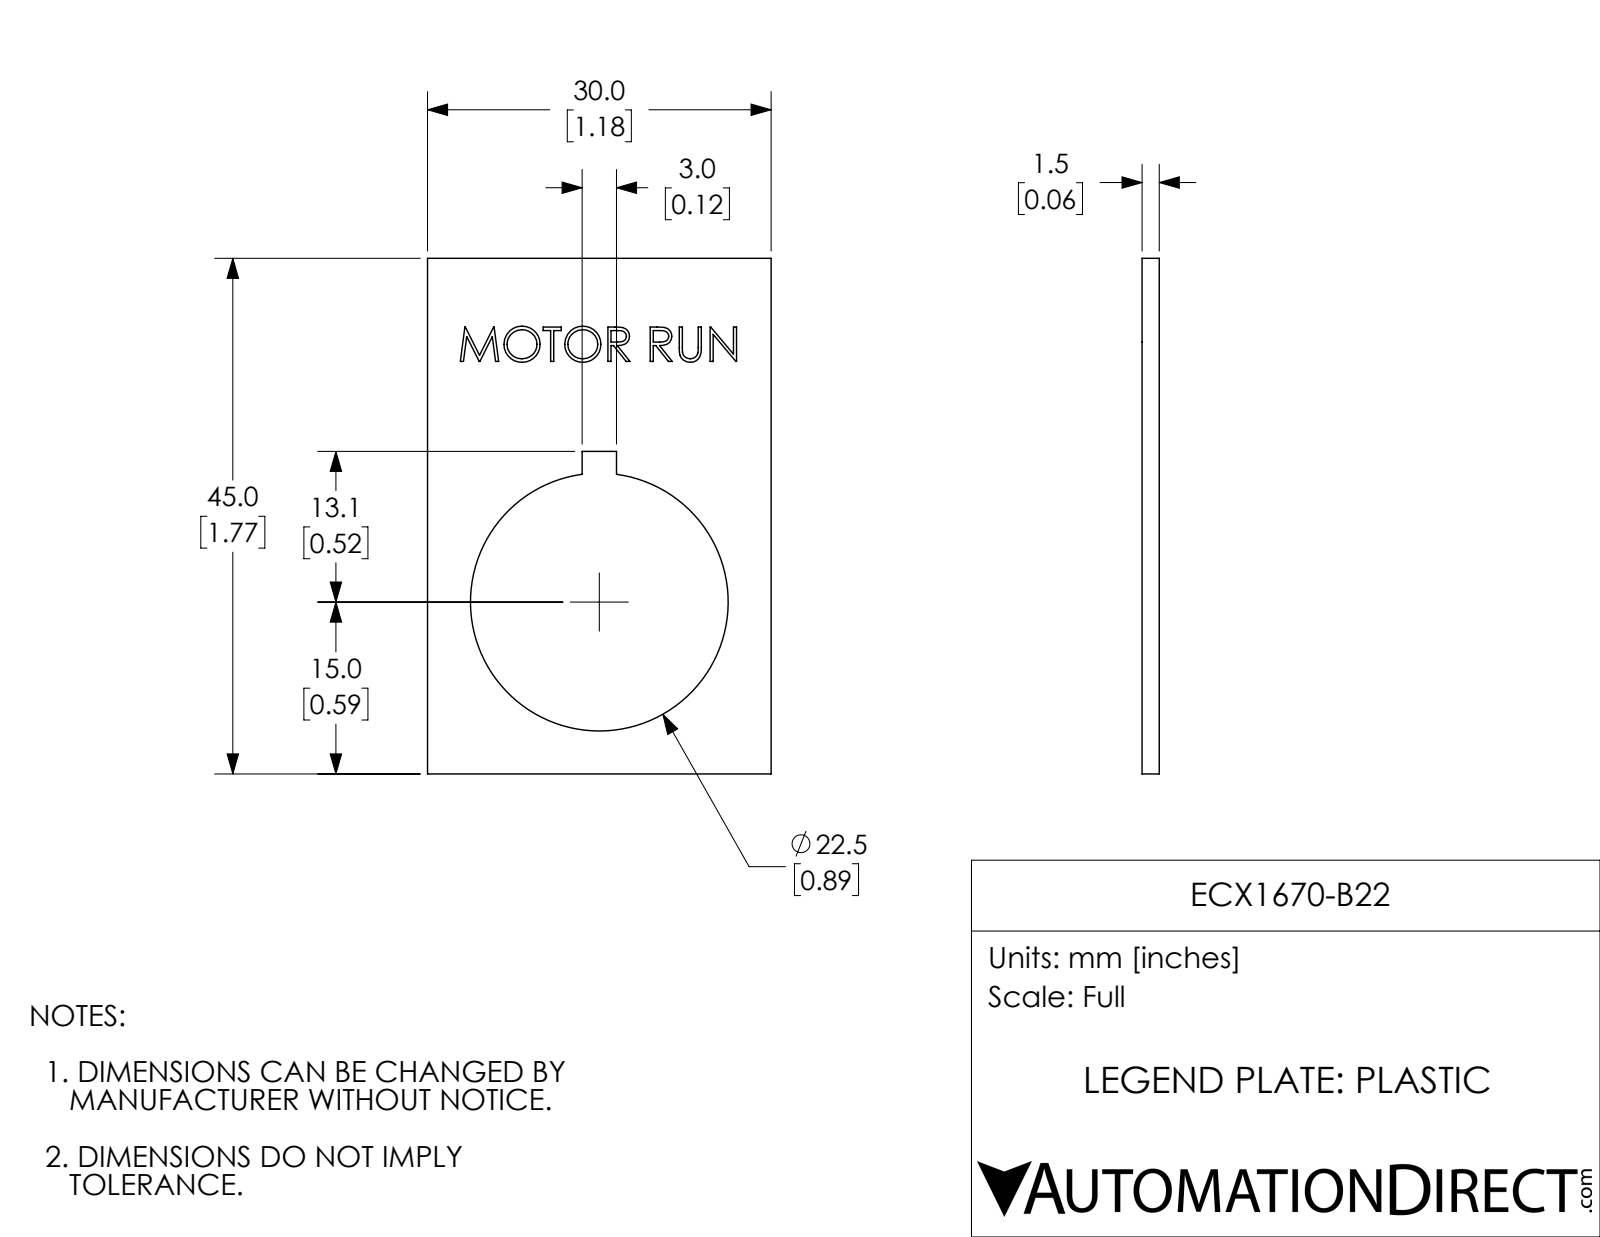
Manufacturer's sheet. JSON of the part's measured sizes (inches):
{"part_name": "ECX1670-B22", "step_written_by": "SolidWorks 2017 (AUTOMOTIVE_DESIGN)", "units": "inches", "bodies": {"solids": 1, "faces": 116, "planar": 80, "cylindrical": 3, "other": 33}, "overall_size": [1.772, 1.181, 0.059], "volume_in3": 0.087, "surface_area_in2": 3.462, "round_holes": [[0.886, 1]], "face_to_face_distances": [0.059, 1.181, 1.772, 0.058, 0.531, 0.65, 1.108, 0.663, 0.118, 0.197]}
